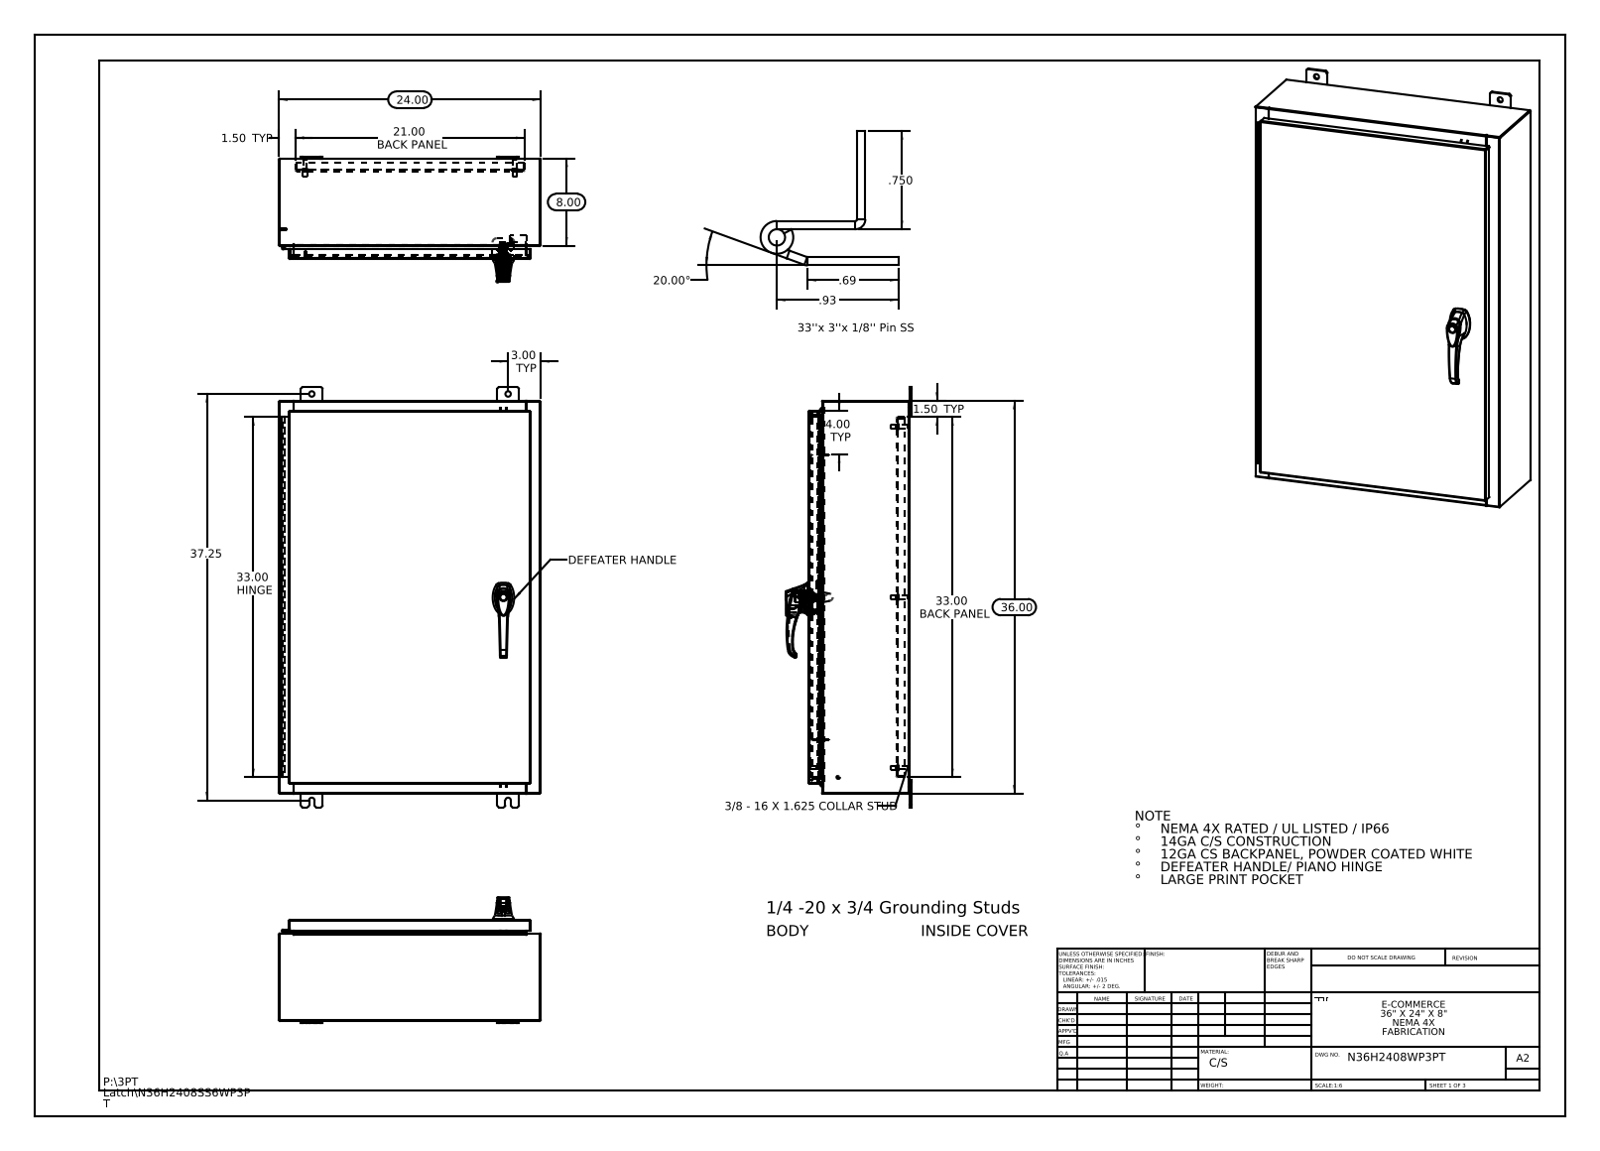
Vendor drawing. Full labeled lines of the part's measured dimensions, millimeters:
Part name (STEP PRODUCT): N36H2408SS6WP3PT Cover; 297025; NMP-SS-RODGUIDES; g26103103_26163303 (+8 more)
STEP written by: SolidWorks 2013 (CONFIG_CONTROL_DESIGN)
Units: millimetres
Bodies: 33 solids, 2770 faces (1035 planar, 1061 cylindrical, 674 other)
Overall size (bounding box): 977.9 × 609.6 × 292
Volume: 5 218 000 mm³ · Surface area: 5 069 000 mm²
Round holes (diameter × count): ⌀12.7 ×10, ⌀6.4 ×4, ⌀3.5 ×3, ⌀4.1 ×3, ⌀2 ×2, ⌀5.2 ×2, ⌀8 ×2, ⌀11.1 ×2, ⌀3.2 ×1, ⌀3.2 ×1, ⌀5 ×1, ⌀7 ×1
Round bosses / shafts (diameter × count): ⌀15.9 ×6, ⌀9.5 ×6, ⌀8.4 ×6, ⌀30 ×1, ⌀19 ×1, ⌀17.3 ×1, ⌀16.8 ×1, ⌀16.2 ×1
Partial cylindrical surfaces — rounded edges, fillets, slot ends (radius × count): R3 ×37, R0.2 ×33, R0.3 ×24, R4.8 ×24, R2.2 ×18, R1 ×15, R0.7 ×12, R0.2 ×6
Main face-to-face distances: 1.9, 231.8, 2.6, 229.9, 233.7, 25.4, 27.3, 204.5, 206.4, 29.9
Hole centre spacings: 288.6, 347.2, 396.9, 629.7, 489, 7.5, 15.9, 21.4
